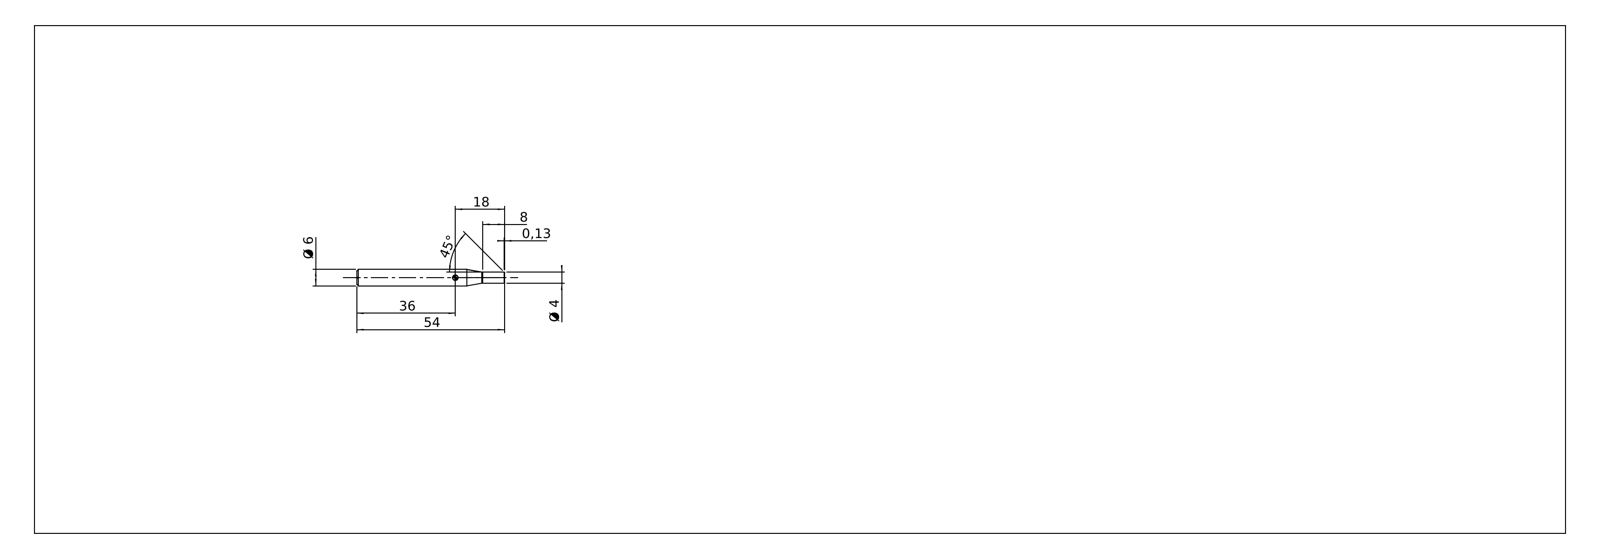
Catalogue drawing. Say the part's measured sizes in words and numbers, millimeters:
The part is named "731.040.00". Its 3-D file was written by "SolidWorks 2019 (CONFIG_CONTROL_DESIGN)". It is 2 solids with 10 faces: 4 planar, 2 cylindrical and 4 other. Overall it measures 54 by 6 by 6 millimeters. Its volume is 1 348 cubic millimeters and its surface area 1 008 square millimeters. Round bosses or shafts: 1 of diameter 6, 1 of diameter 4. The main face-to-face distances are 46, 8, 54.
